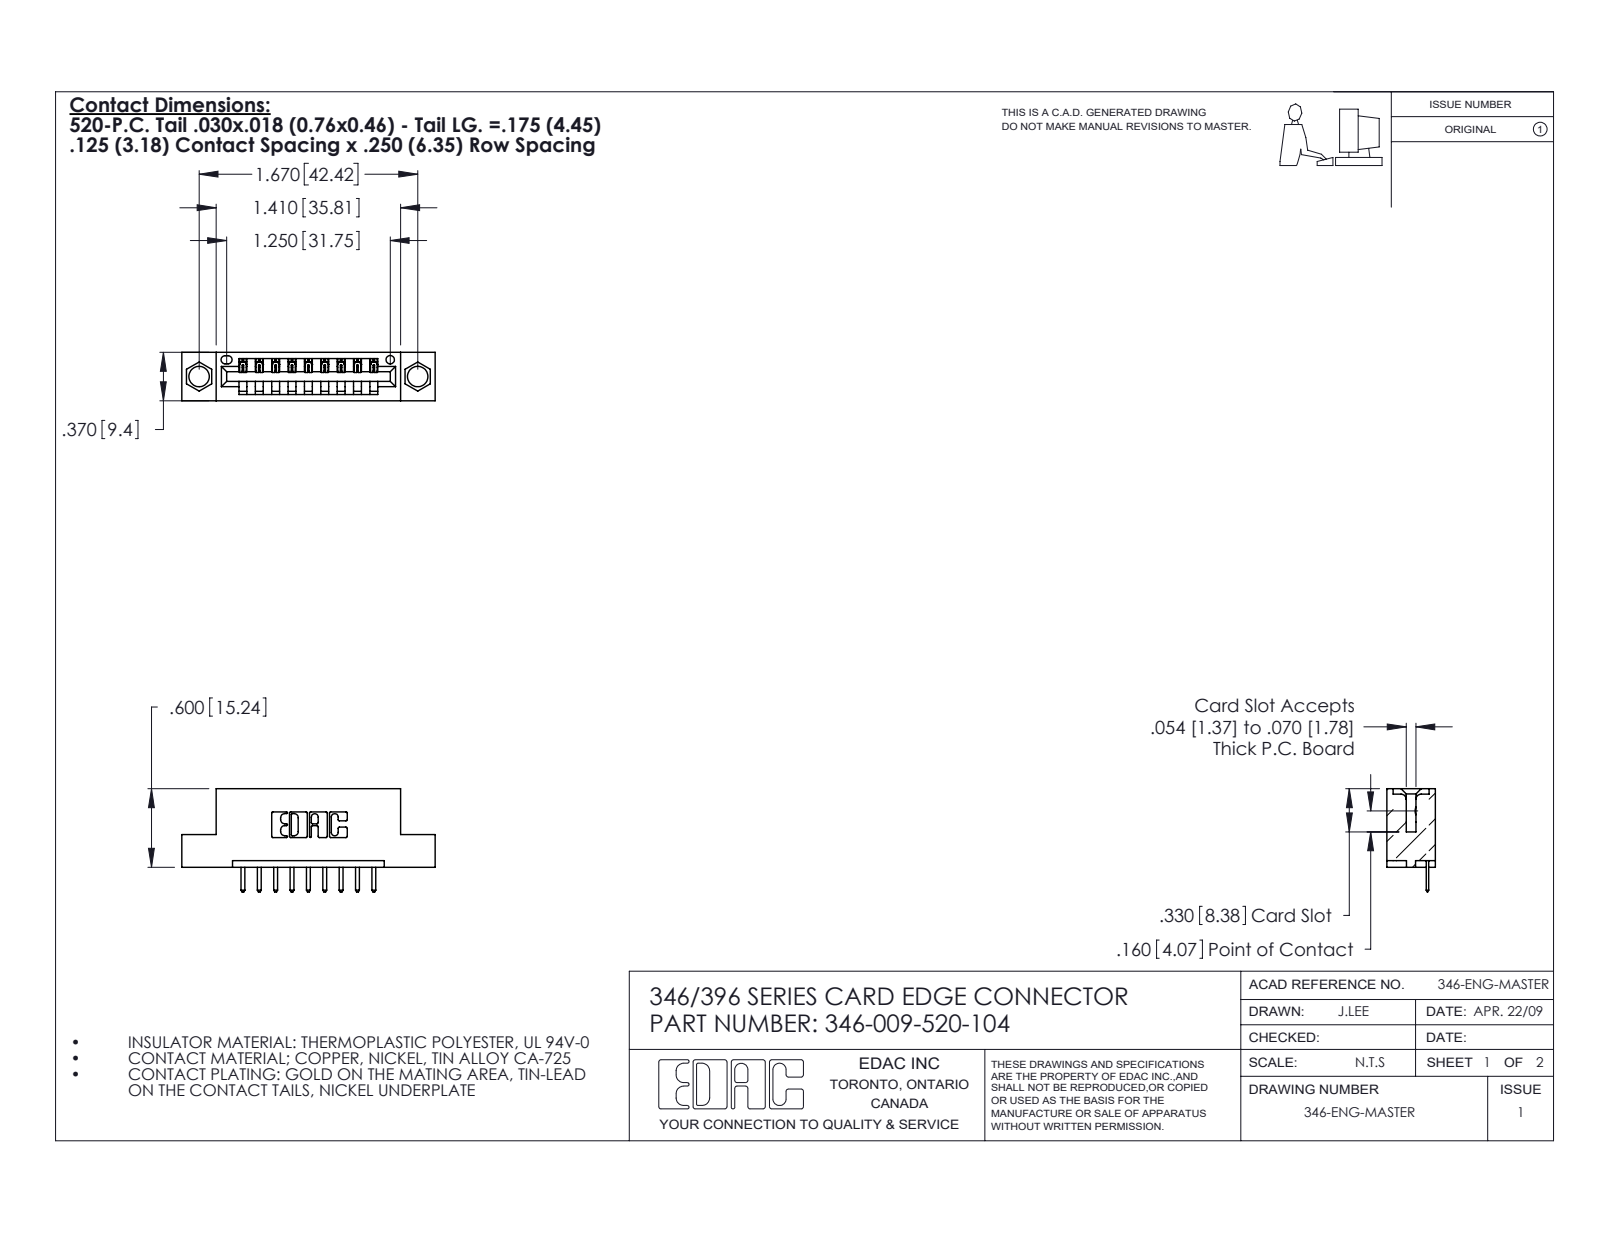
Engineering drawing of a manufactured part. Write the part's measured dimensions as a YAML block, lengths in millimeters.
part_name: "346-009-520-104; 345-292-001_345-293-120; 346 Part_Flush Mounting Lugs - 0.156 Dia-TH"
step_written_by: "SolidWorks 2020 (CONFIG_CONTROL_DESIGN)"
units: millimeters
bodies: {solids: 10, faces: 694, planar: 468, cylindrical: 226, other: 0}
overall_size: [49.1, 20, 9.4]
volume: 4340
surface_area: 4826
round_holes:
  - {diameter: 4, count: 2}
  - {diameter: 1.6, count: 1}
partial_cylinders:
  - {radius: 0.3, count: 22}
  - {radius: 0.3, count: 20}
  - {radius: 0.2, count: 18}
  - {radius: 0.2, count: 6}
  - {radius: 0.8, count: 6}
  - {radius: 0.7, count: 3}
  - {radius: 0.8, count: 2}
  - {radius: 1, count: 2}
face_to_face_distances: [6.4, 9.4, 1.2, 8.2, 3.8, 5.6, 2.5, 4.4, 3.2, 12.7]
hole_center_spacings: [6.2, 37.2, 42.4]
